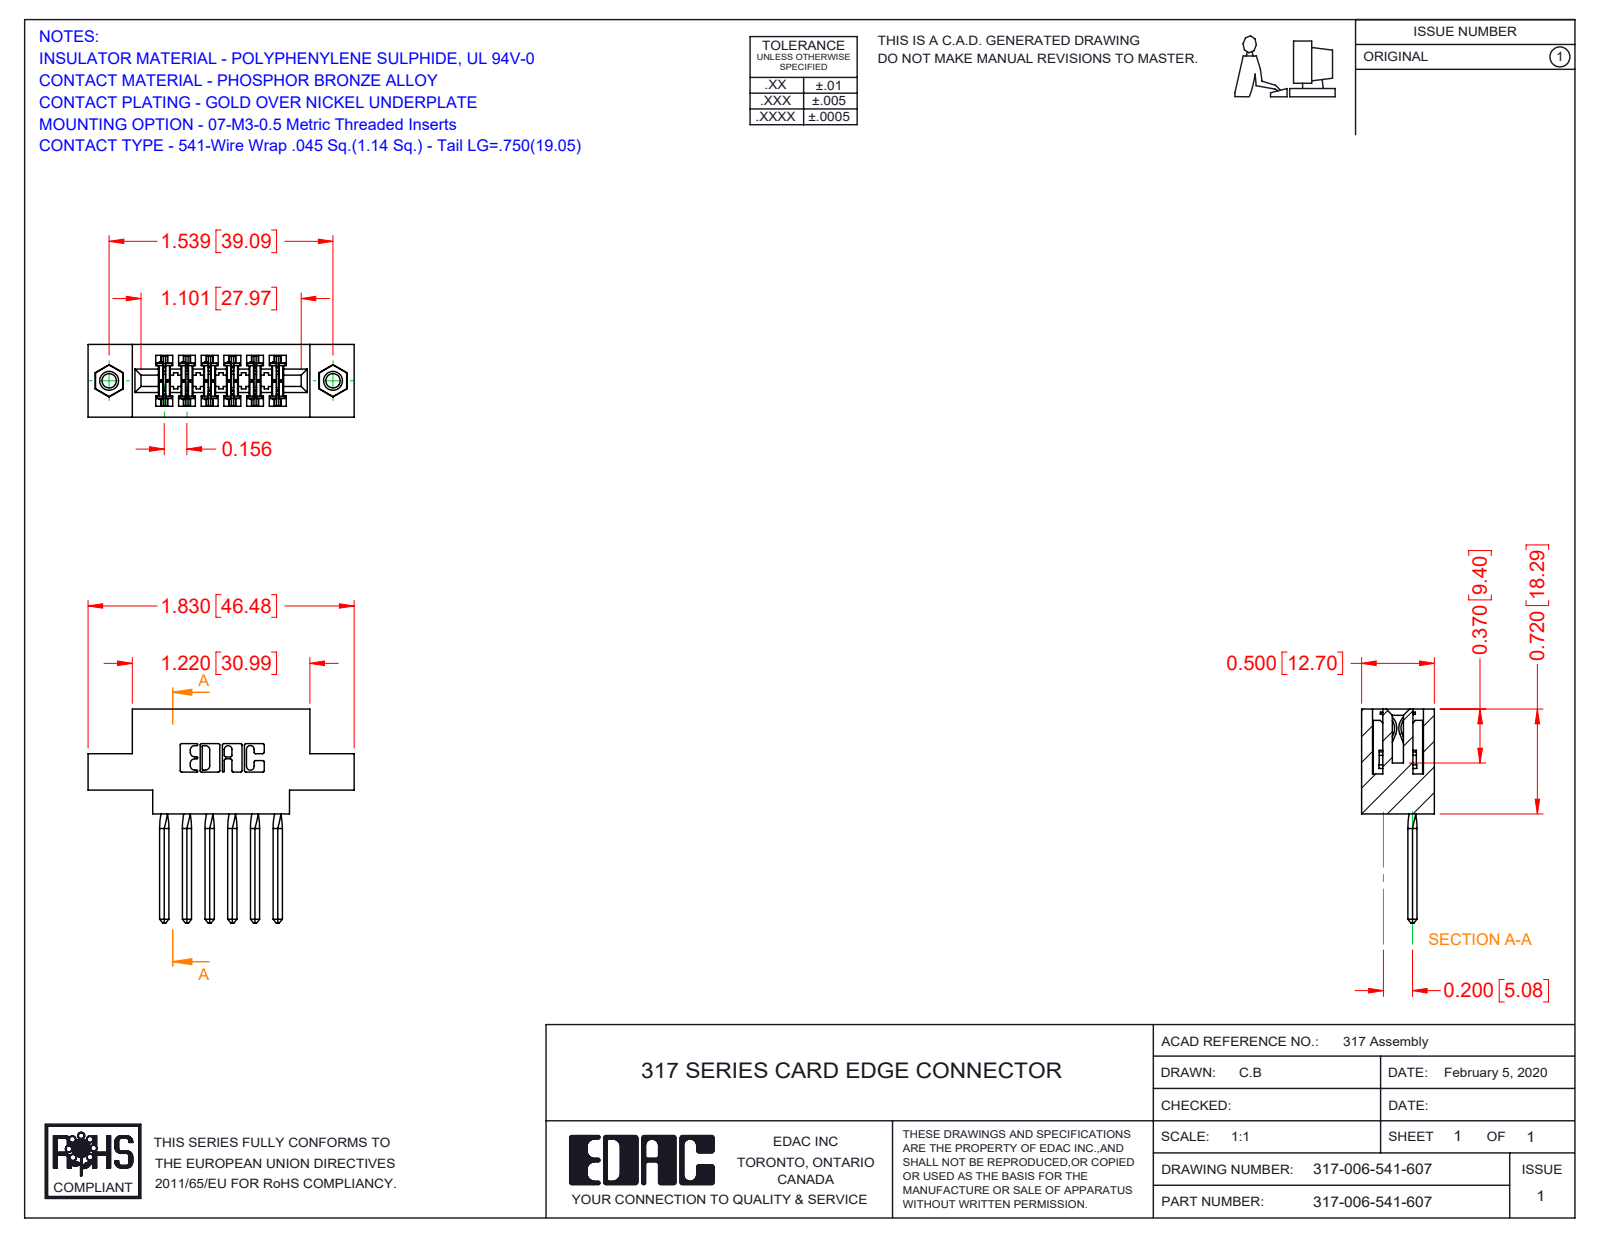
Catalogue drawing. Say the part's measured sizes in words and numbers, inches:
The part is named "317-006-541-607; 345-250-001_345-250-005-103; 317-290-002_541; 317 Part_.156 Dia - TI". Its 3-D file was written by "SolidWorks 2016 (CONFIG_CONTROL_DESIGN)". It is 9 solids with 1074 faces: 834 planar, 200 cylindrical and 40 other. Overall it measures 1.83 by 1.47 by 0.5 inches. Its volume is 0.392 cubic inches and its surface area 12.25 square inches. Round holes: 2 of diameter 0.098, 2 of diameter 0.125, 2 of diameter 0.156. Round bosses or shafts: 2 of diameter 0.155. Partial cylindrical surfaces (rounded edges, fillets, slot ends): 22 of radius 0.01, 12 of radius 0.015, 6 of radius 0.007, 6 of radius 0.031, 3 of radius 0.026, 2 of radius 0.095, 2 of radius 0.1, 2 of radius 0.11. The main face-to-face distances are 0.5, 0.075, 0.425, 0.11, 0.156, 0.065, 0.116, 0.163, 0.136, 0.22. The hole center spacings are 1.539.
